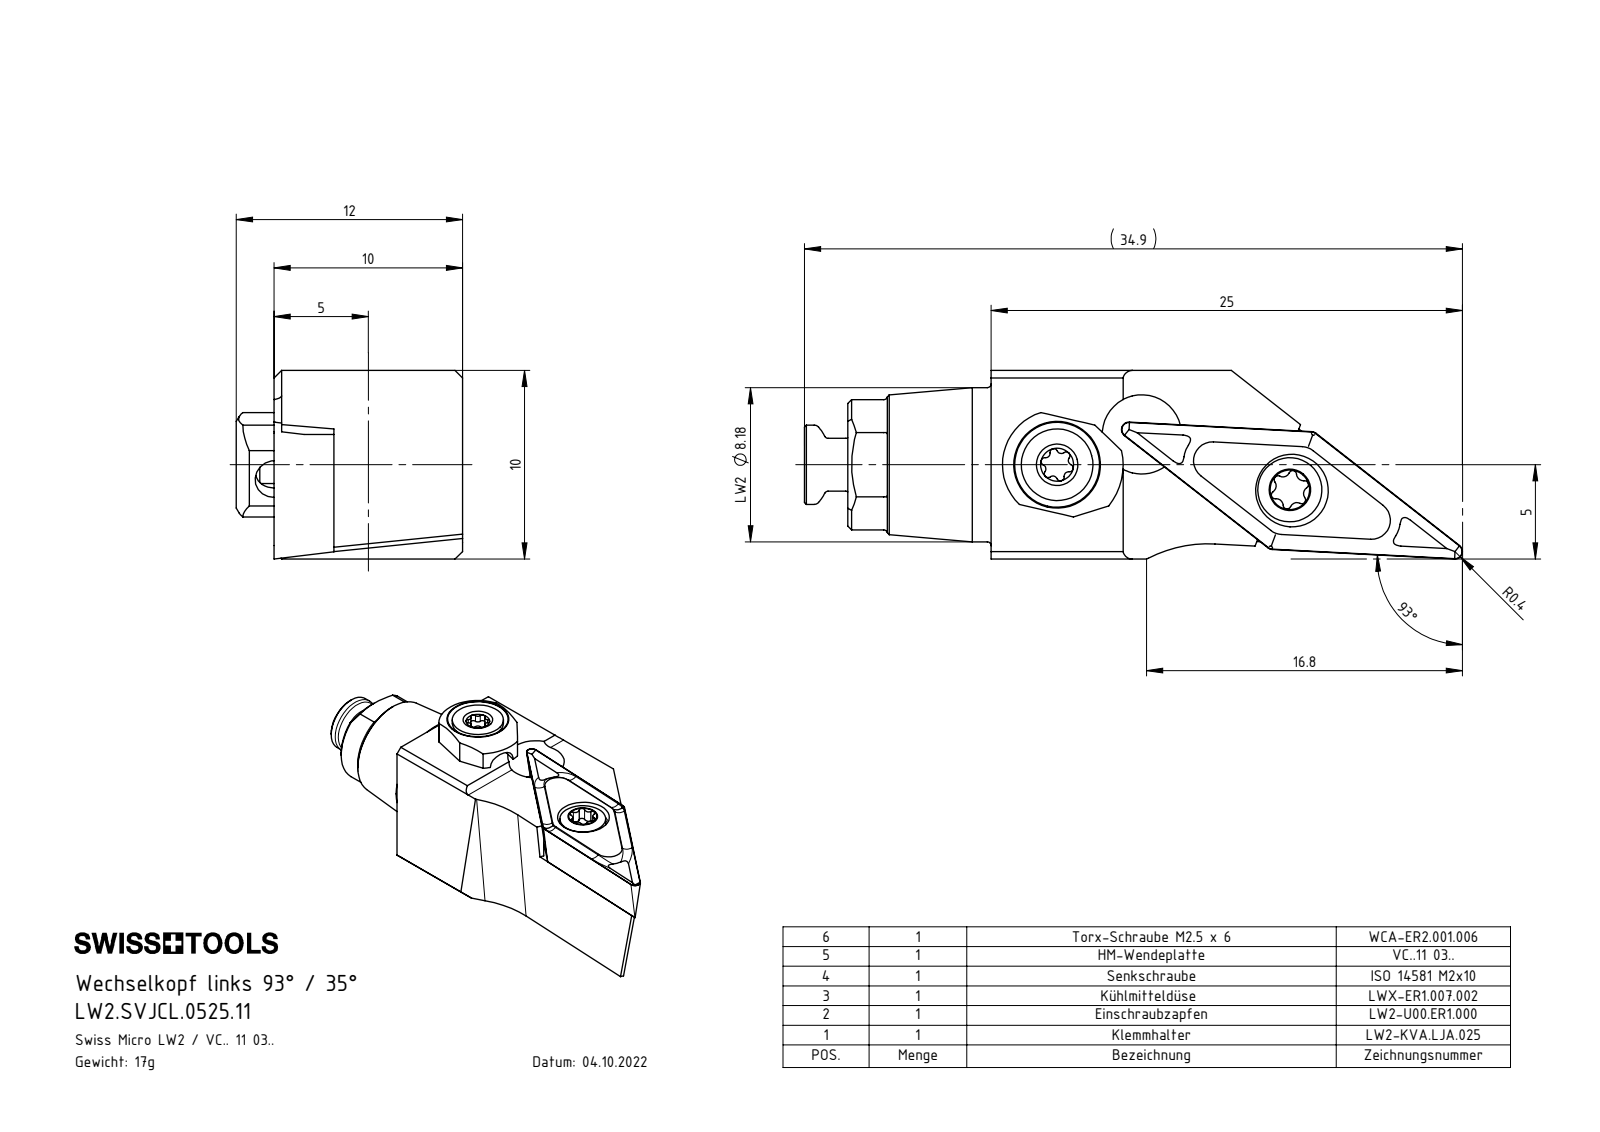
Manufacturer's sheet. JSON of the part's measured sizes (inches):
{"part_name": "WCA-ER2.001.006_B; LW2-U00.ER1.000_A; LW2-KVA.LJA.025_A; ISO 14581 - M2x10 (+3 more)", "step_written_by": "SolidWorks 2022 (CONFIG_CONTROL_DESIGN)", "units": "inches", "bodies": {"solids": 6, "faces": 259, "planar": 65, "cylindrical": 94, "other": 100}, "overall_size": [1.374, 0.472, 0.394], "volume_in3": 0.121, "surface_area_in2": 3.016, "round_holes": [[0.039, 1], [0.059, 1], [0.063, 1], [0.081, 1], [0.11, 1], [0.118, 1], [0.138, 1], [0.152, 1], [0.165, 1]], "round_bosses_or_shafts": [[0.322, 1], [0.165, 1], [0.157, 1], [0.15, 1], [0.134, 1], [0.118, 1], [0.11, 1], [0.098, 1]], "partial_cylinders_radius": [[0.008, 8], [0.007, 6], [0.008, 6], [0.009, 6], [0.011, 6], [0.014, 5], [0.014, 1], [0.02, 1]], "face_to_face_distances": [0.394, 0.269, 0.125, 0.378, 0.109, 0.016, 0.299, 0.079, 0.043, 0.315], "hole_center_spacings": [0.188, 0.33, 0.335, 0.489, 0.494]}
